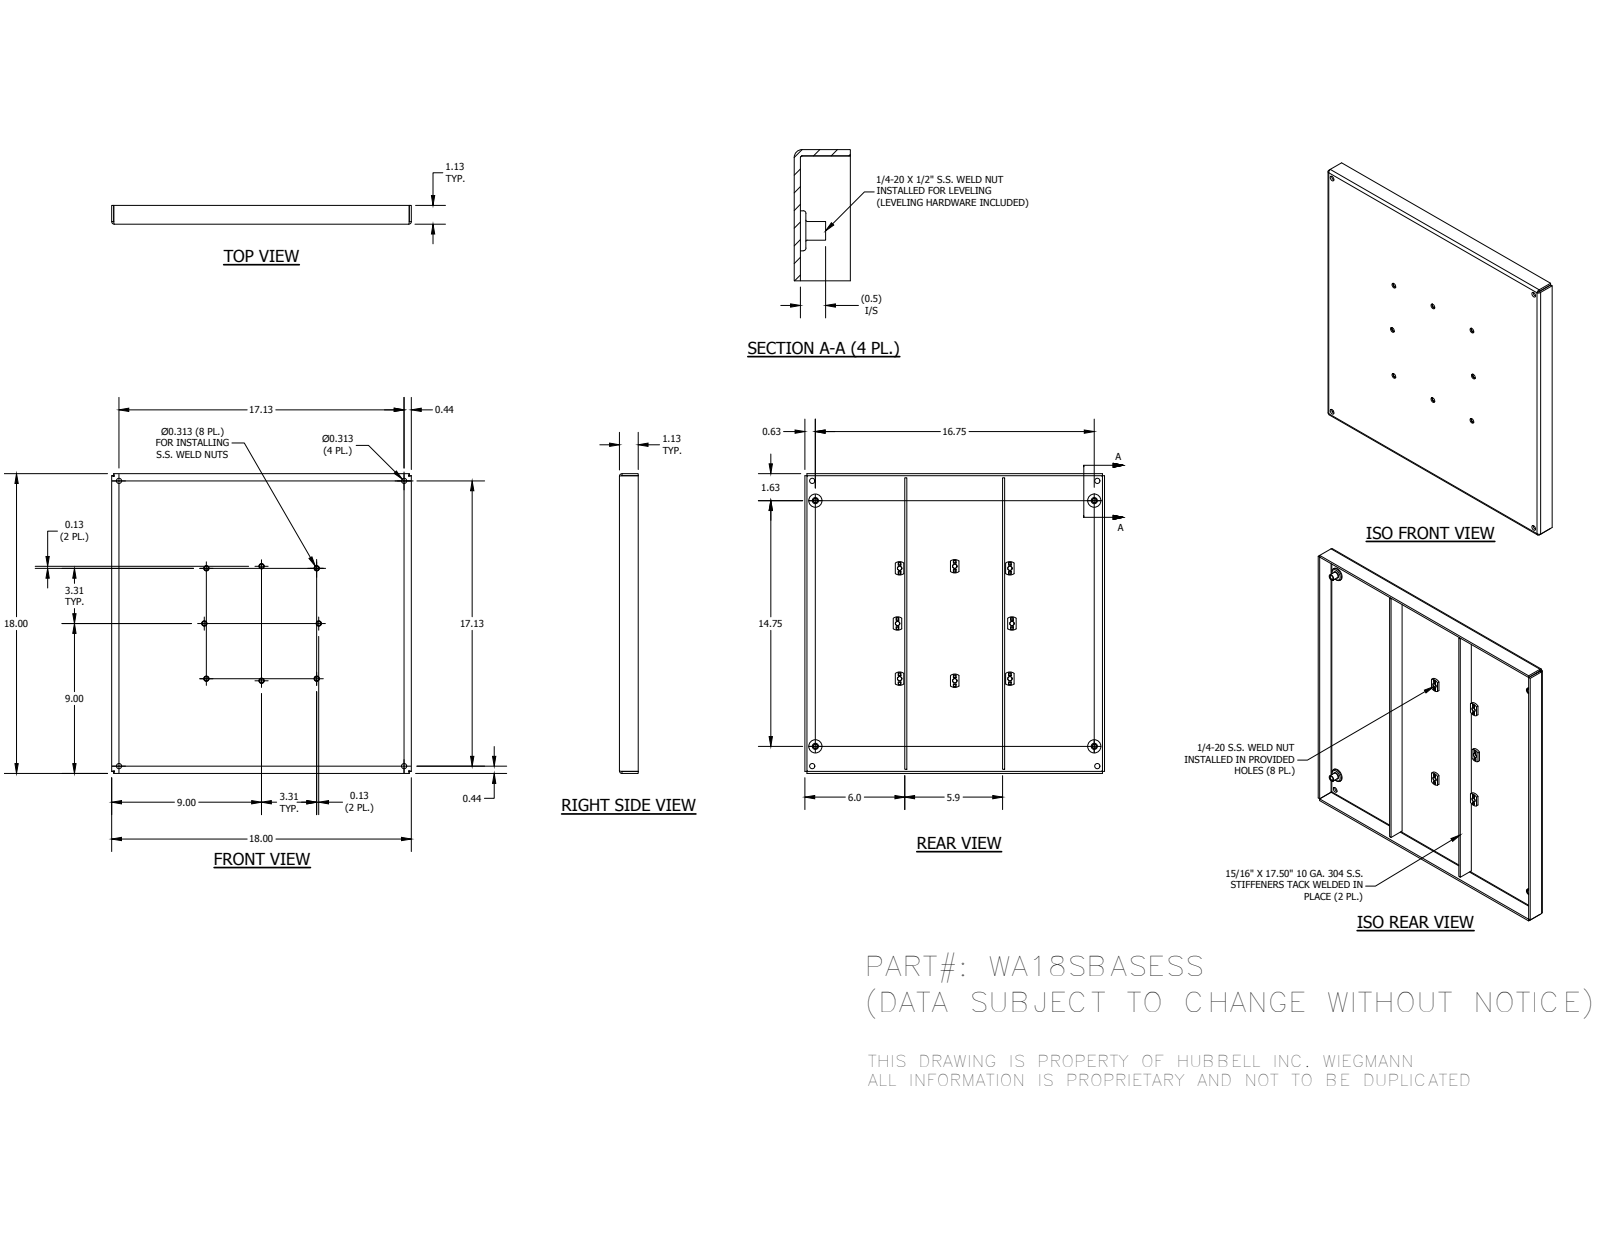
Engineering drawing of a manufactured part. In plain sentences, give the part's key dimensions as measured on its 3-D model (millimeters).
The part is named "WA18SBASEBSS; WA18SBASESSSTFNR; 349122; HFW349157 (+1 more)". Its 3-D file was written by "Autodesk Inventor 2016 (AUTOMOTIVE_DESIGN)". It is 15 solids with 346 faces: 210 planar, 80 cylindrical and 56 other. Overall it measures 457.2 by 457.2 by 28.57 millimeters. Its volume is 878 666 cubic millimeters and its surface area 571 624 square millimeters. Round holes: 12 of diameter 6.35, 12 of diameter 7.94. Round bosses or shafts: 8 of diameter 7.54, 4 of diameter 20.32, 4 of diameter 9.52. Partial cylindrical surfaces (rounded edges, fillets, slot ends): 10 of radius 2.45, 8 of radius 10.31, 4 of radius 0.79, 4 of radius 3.97. The main face-to-face distances are 3.18, 152.4, 3.17, 454.03, 301.62, 149.22, 457.2, 155.58, 304.8, 450.85. The hole center spacings are 84.2, 190.98, 253.47, 329.79, 374.44, 123.47, 168.28, 188.59.
